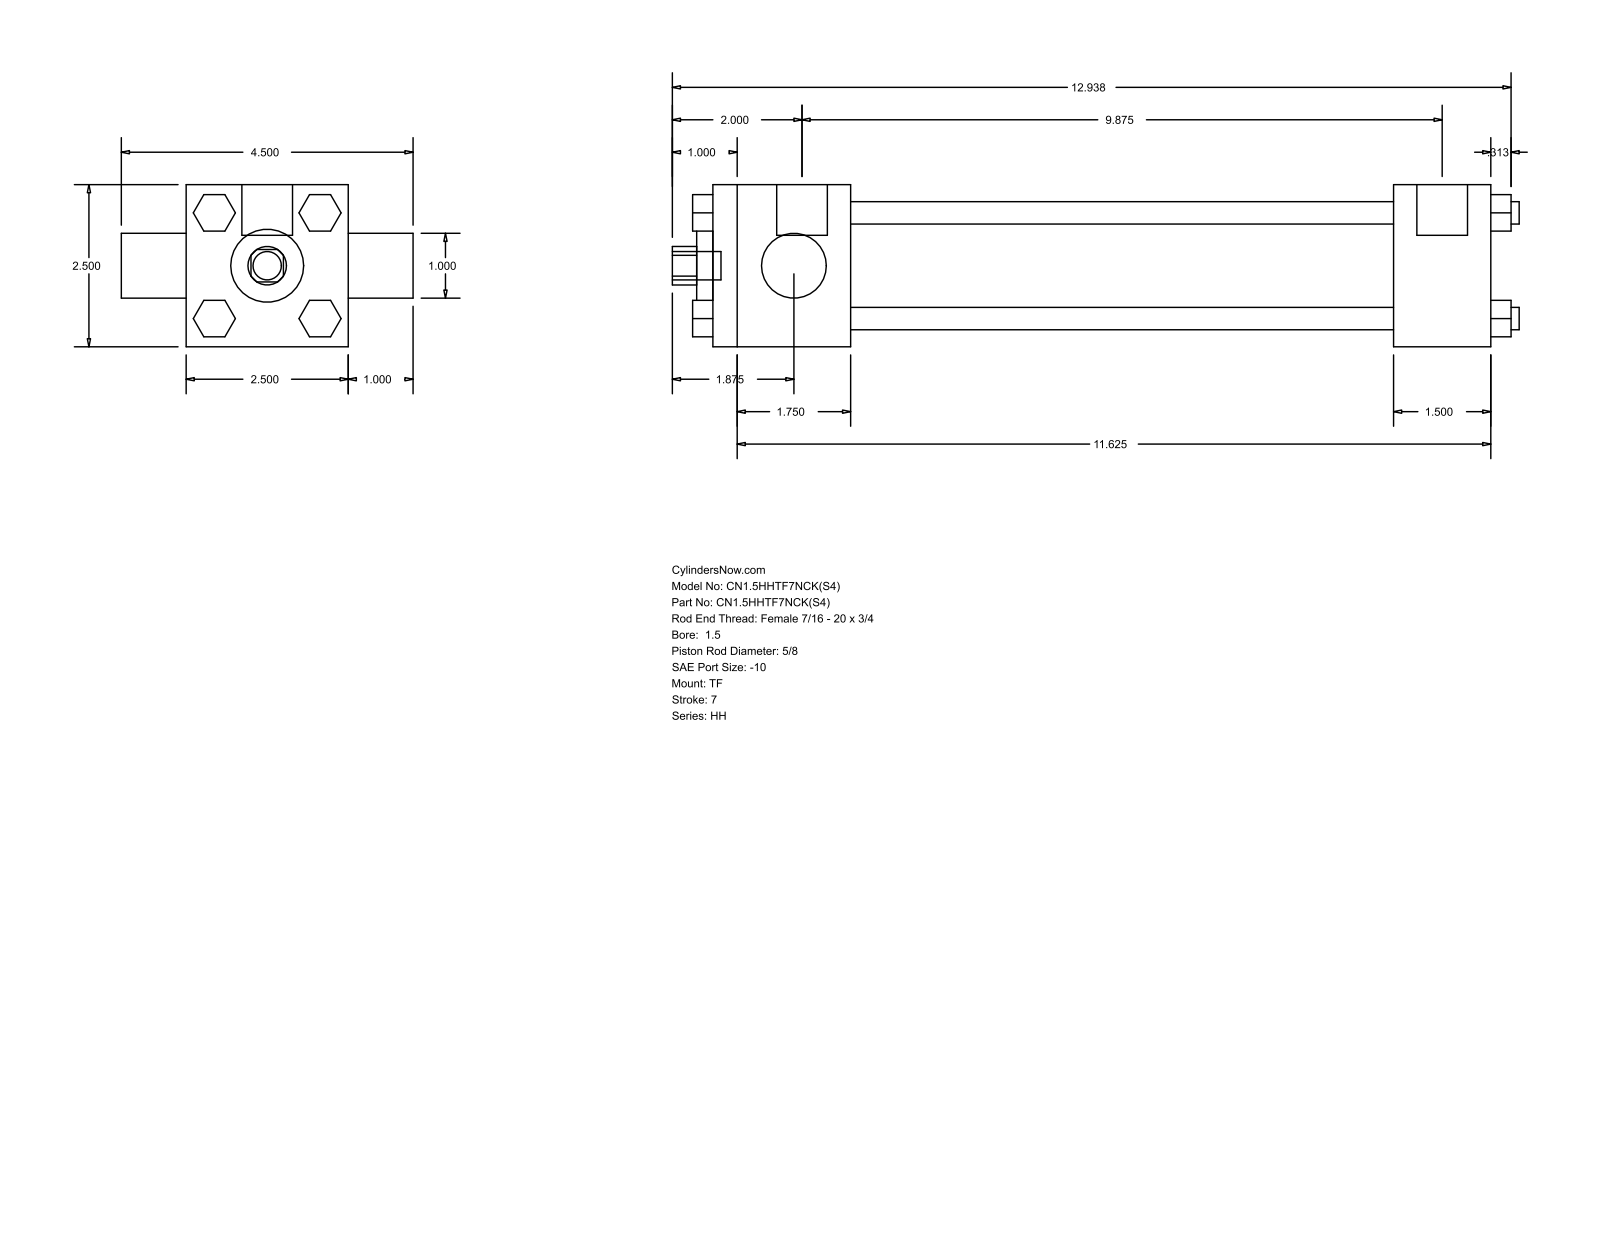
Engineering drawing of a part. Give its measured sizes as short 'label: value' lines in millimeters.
name: HH_TF__0150_0.625
written by: GSSL Pune (CONFIG_CONTROL_DESIGN)
unit: mm
bodies: 0 solids, 120 faces (92 planar, 28 cylindrical, 0 other)
size: 331.79 × 114.3 × 63.5
holes: 1× ⌀15.88, 1× ⌀25.4, 1× ⌀28.57, 1× ⌀44.45
bosses: 4× ⌀8.76, 3× ⌀5.56, 2× ⌀19.84, 1× ⌀11.11
rounds: 1× R7.54
face distances: 63.5, 304.8, 53.97, 250.83, 266.69, 212.72, 38.11, 25.4, 20.7, 14.29
